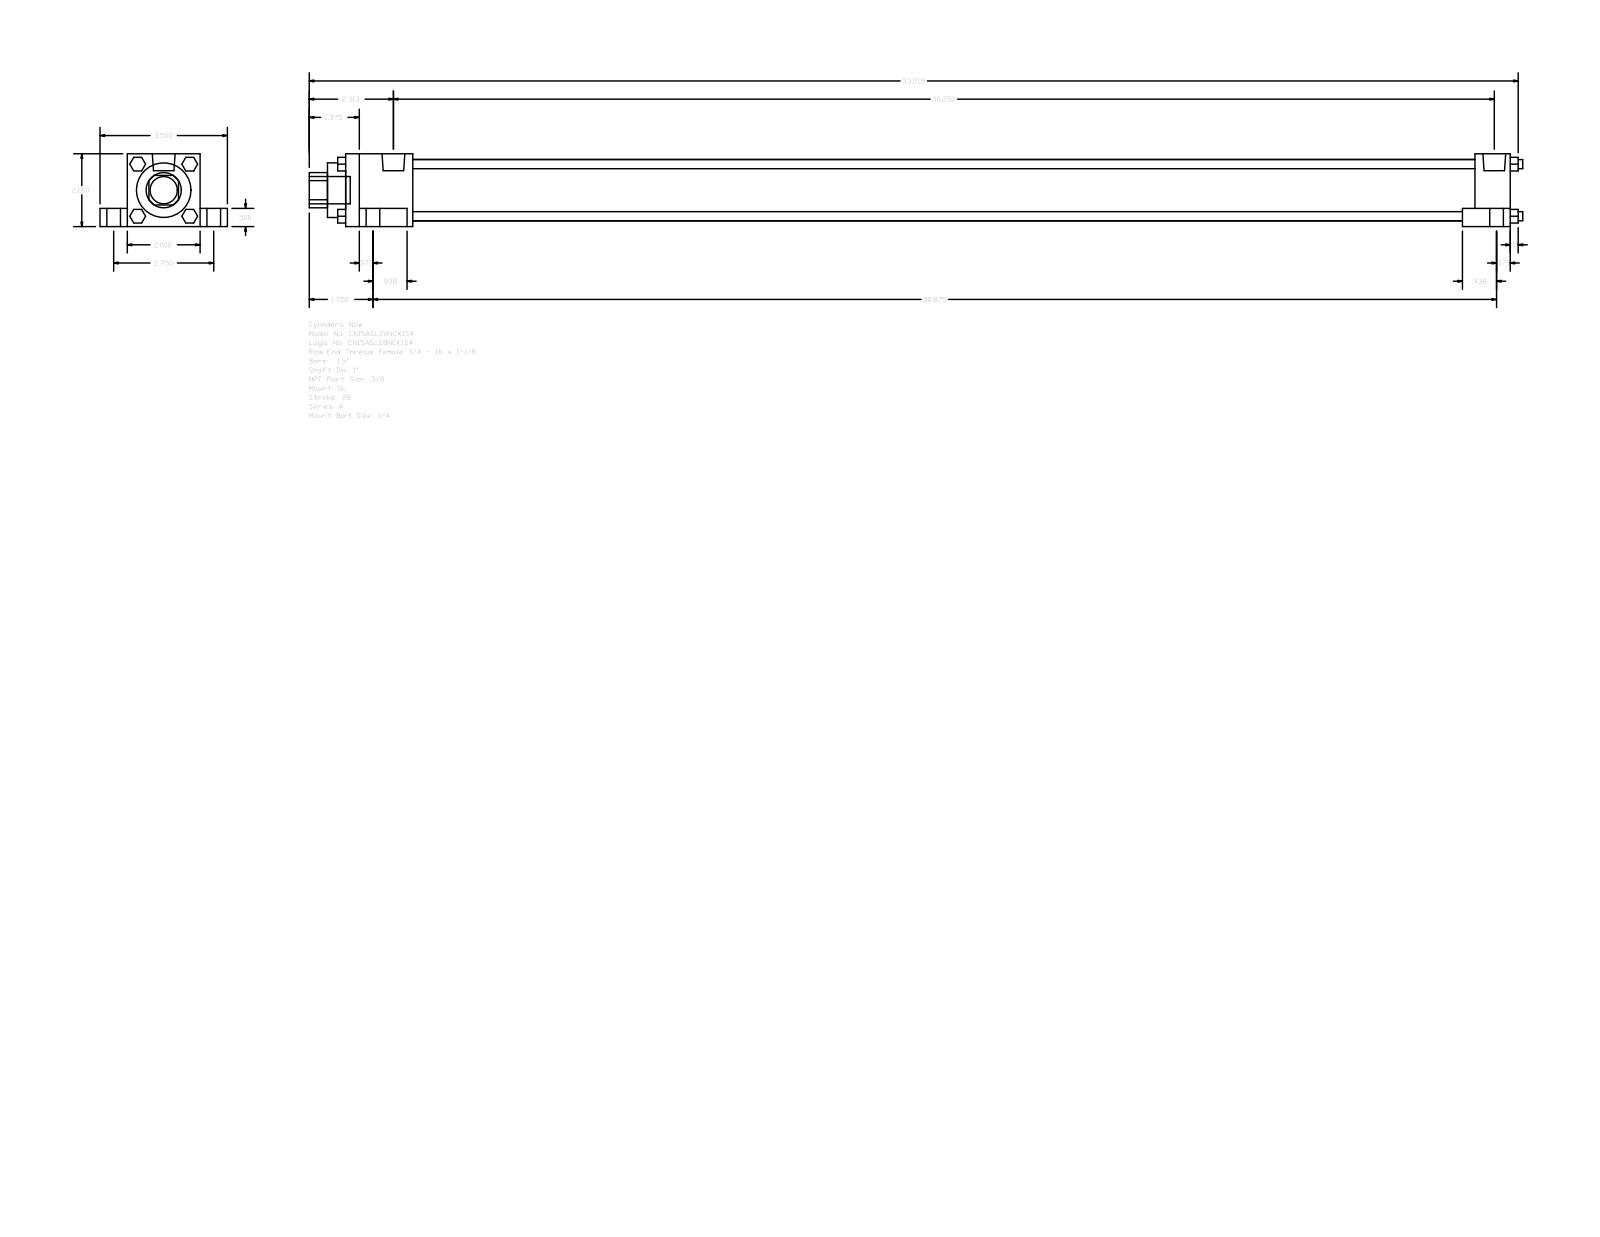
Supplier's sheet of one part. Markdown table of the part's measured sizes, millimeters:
| quantity | value |
| --- | --- |
| part name | A_SL__0150_1 |
| STEP written by | GSSL Pune (CONFIG_CONTROL_DESIGN) |
| units | millimeters |
| bodies | 0 solids, 148 faces (112 planar, 36 cylindrical, 0 other) |
| overall size | 846.93 × 88.9 × 50.8 |
| round holes (diameter × count) | 25.4 × 1, 38.1 × 1, 42.93 × 1 |
| round bosses / shafts (diameter × count) | 15.88 × 4, 9.53 × 4, 6.35 × 4, 5.56 × 4, 15.93 × 2, 19.05 × 1 |
| partial cylindrical surfaces (radius × count) | 12.29 × 1 |
| main face-to-face distances | 50.8, 12.7, 38.1, 19.05, 69.85, 9.52, 812.8, 33.34, 788.19, 24.61 |
